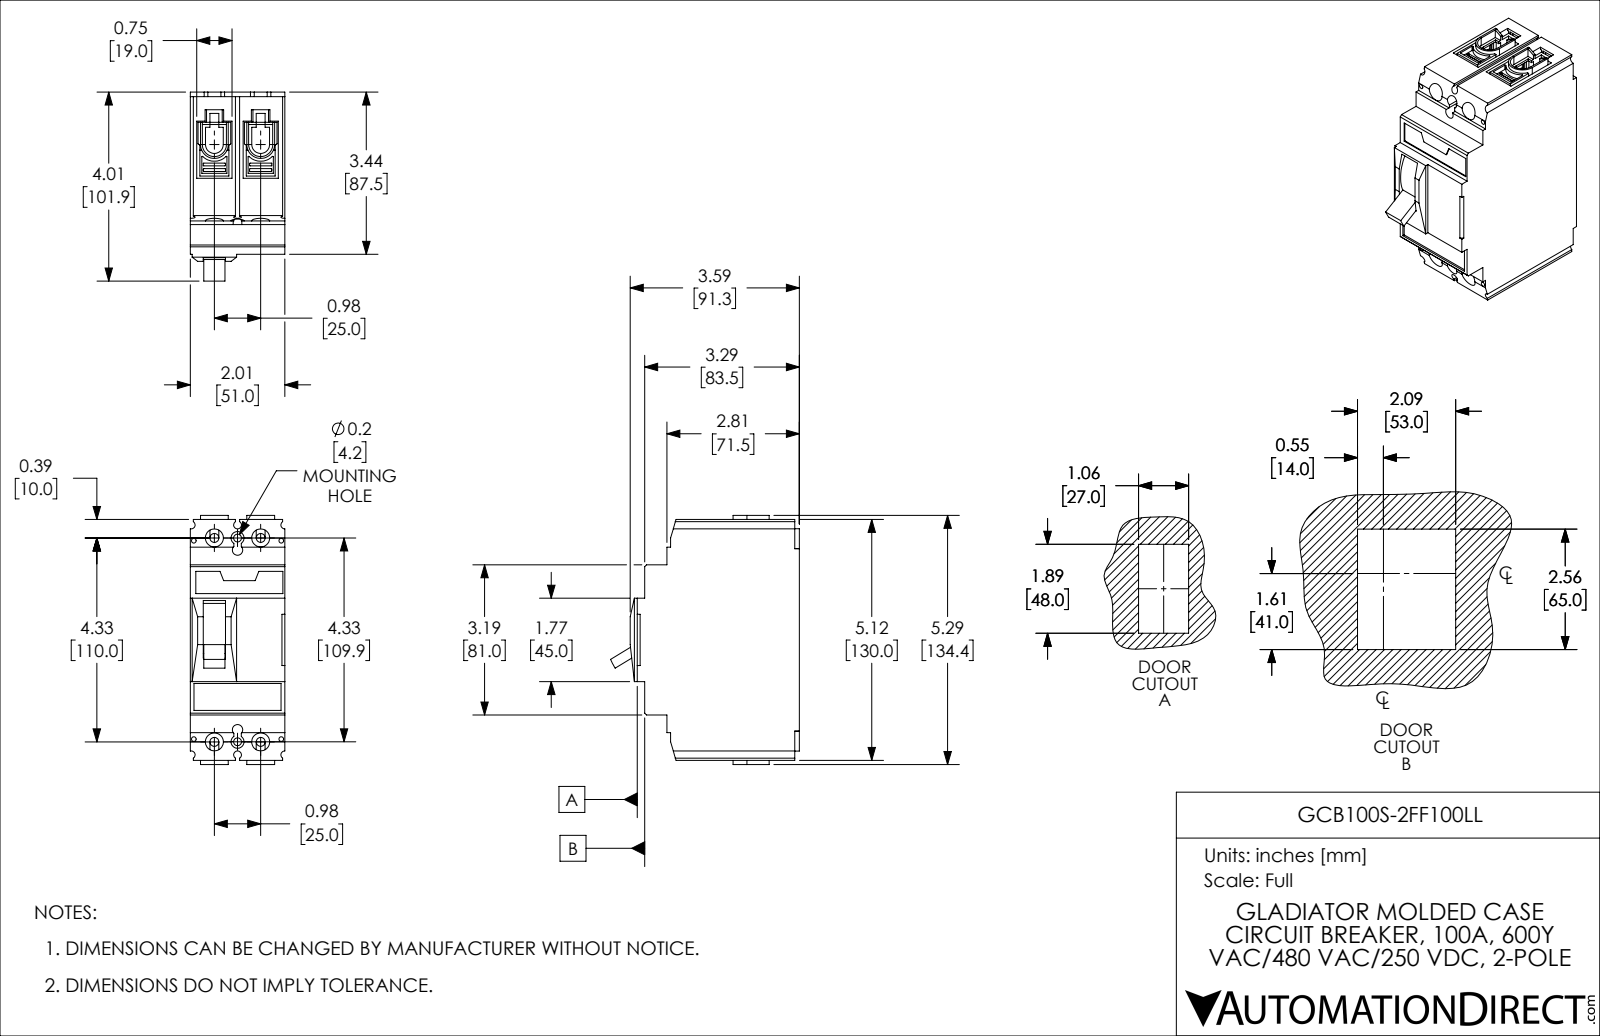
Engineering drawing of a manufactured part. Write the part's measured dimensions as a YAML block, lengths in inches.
part_name: "GCB100S-2FF100LL"
step_written_by: "SolidWorks 2021 (CONFIG_CONTROL_DESIGN)"
units: inches
bodies: {solids: 1, faces: 839, planar: 529, cylindrical: 278, other: 32}
overall_size: [5.291, 4.013, 2.008]
volume: 29.1
surface_area: 110.4
round_holes:
  - {diameter: 0.098, count: 4}
  - {diameter: 0.165, count: 4}
  - {diameter: 0.189, count: 4}
  - {diameter: 0.382, count: 4}
  - {diameter: 0.276, count: 2}
partial_cylinders:
  - {radius: 0.012, count: 58}
  - {radius: 0.02, count: 26}
  - {radius: 0.039, count: 10}
  - {radius: 0.157, count: 10}
  - {radius: 0.024, count: 4}
  - {radius: 0.083, count: 4}
  - {radius: 0.11, count: 2}
  - {radius: 0.189, count: 2}
face_to_face_distances: [2.008, 0.984, 0.622, 4.496, 0.748, 1.87, 0.11, 0.886, 1.122, 0.138]
hole_center_spacings: [0.441, 0.492, 0.564, 0.931, 0.987, 1.422, 4.294, 4.357]
